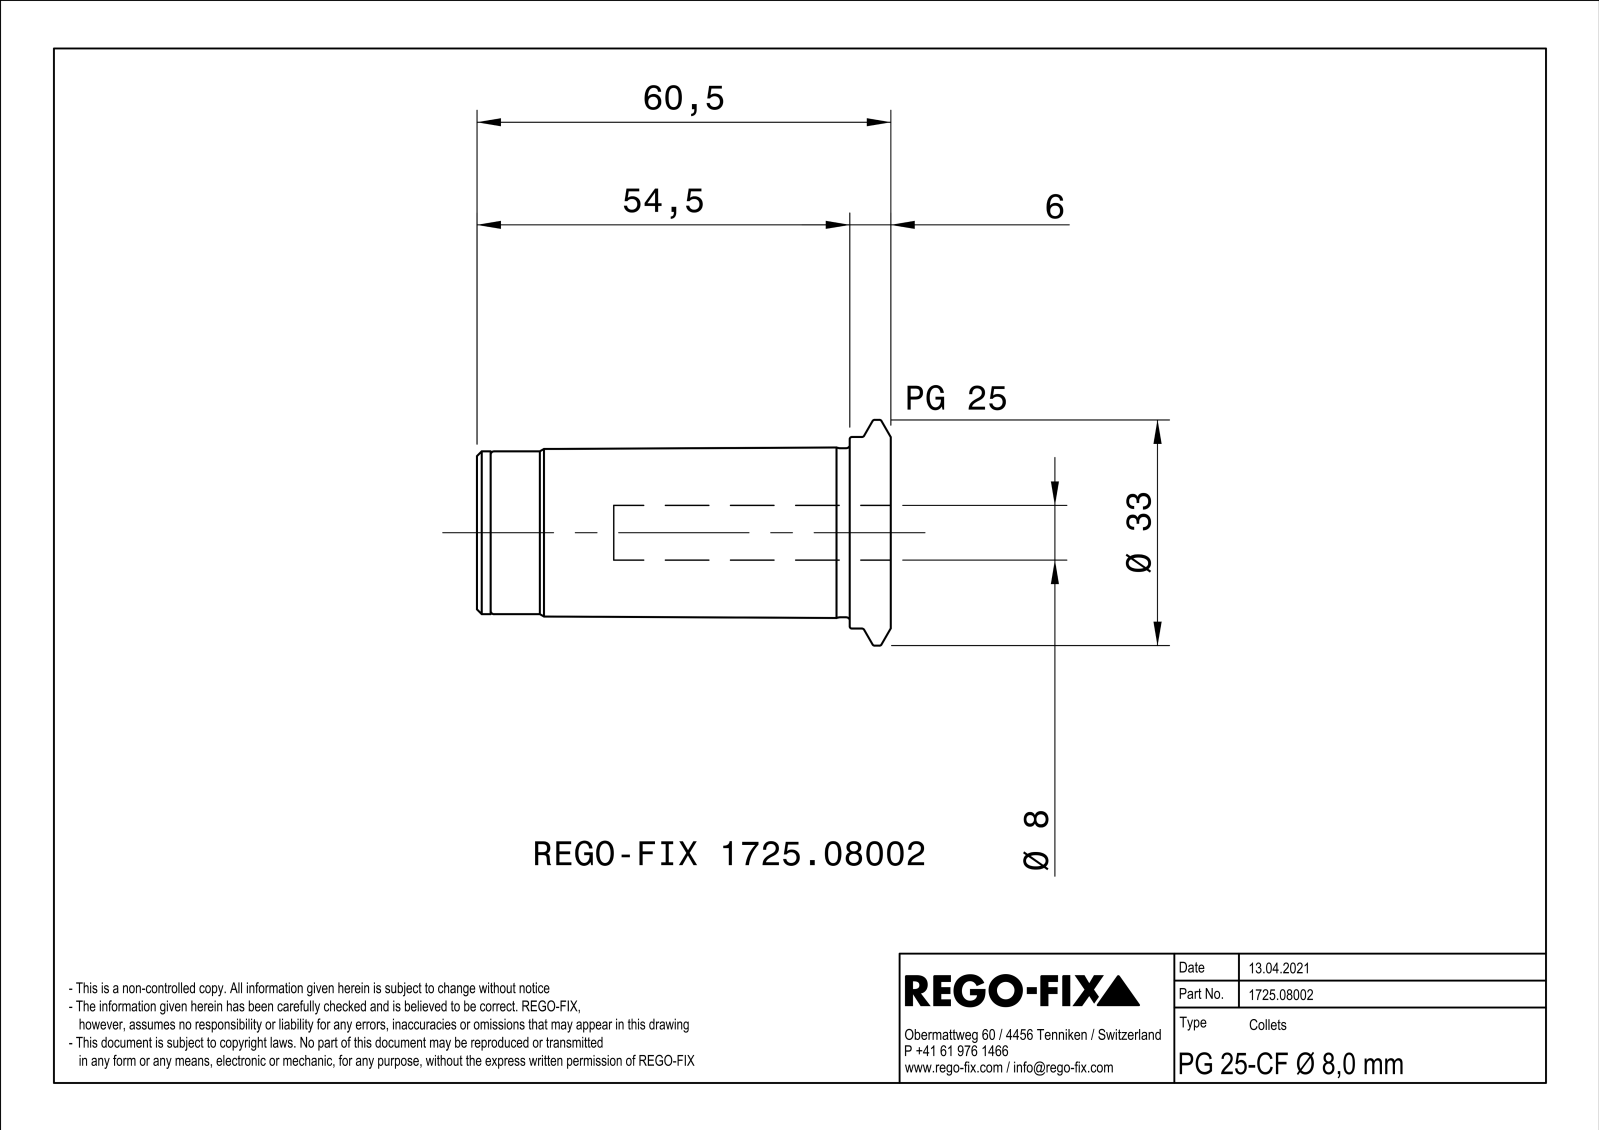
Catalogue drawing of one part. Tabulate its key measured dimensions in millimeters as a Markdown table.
| quantity | value |
| --- | --- |
| part name | NOCUT |
| STEP written by | SIEMENS PLM Software Solid Edge ST10 (AUTOMOTIVE_DESIGN) |
| units | millimeters |
| bodies | 1 solid, 89 faces (23 planar, 27 cylindrical, 39 other) |
| overall size | 60.5 × 33 × 32.99 |
| volume | 24 983 mm³ |
| surface area | 11 107 mm² |
| round holes (diameter × count) | 2.5 × 3, 5.2 × 1, 6.92 × 1, 8 × 1, 8.2 × 1, 20.92 × 1, 22.2 × 1 |
| round bosses / shafts (diameter × count) | 33 × 1, 28 × 1, 24.7 × 1, 23.8 × 1, 20.4 × 1, 12 × 1 |
| partial cylindrical surfaces (radius × count) | 0.75 × 3 |
| main face-to-face distances | 1, 60.5, 52.6, 7.9, 58.5, 5.9, 2, 50, 2.6, 8.5 |
| hole center spacings | 7.75, 13.43, 13.42 |
